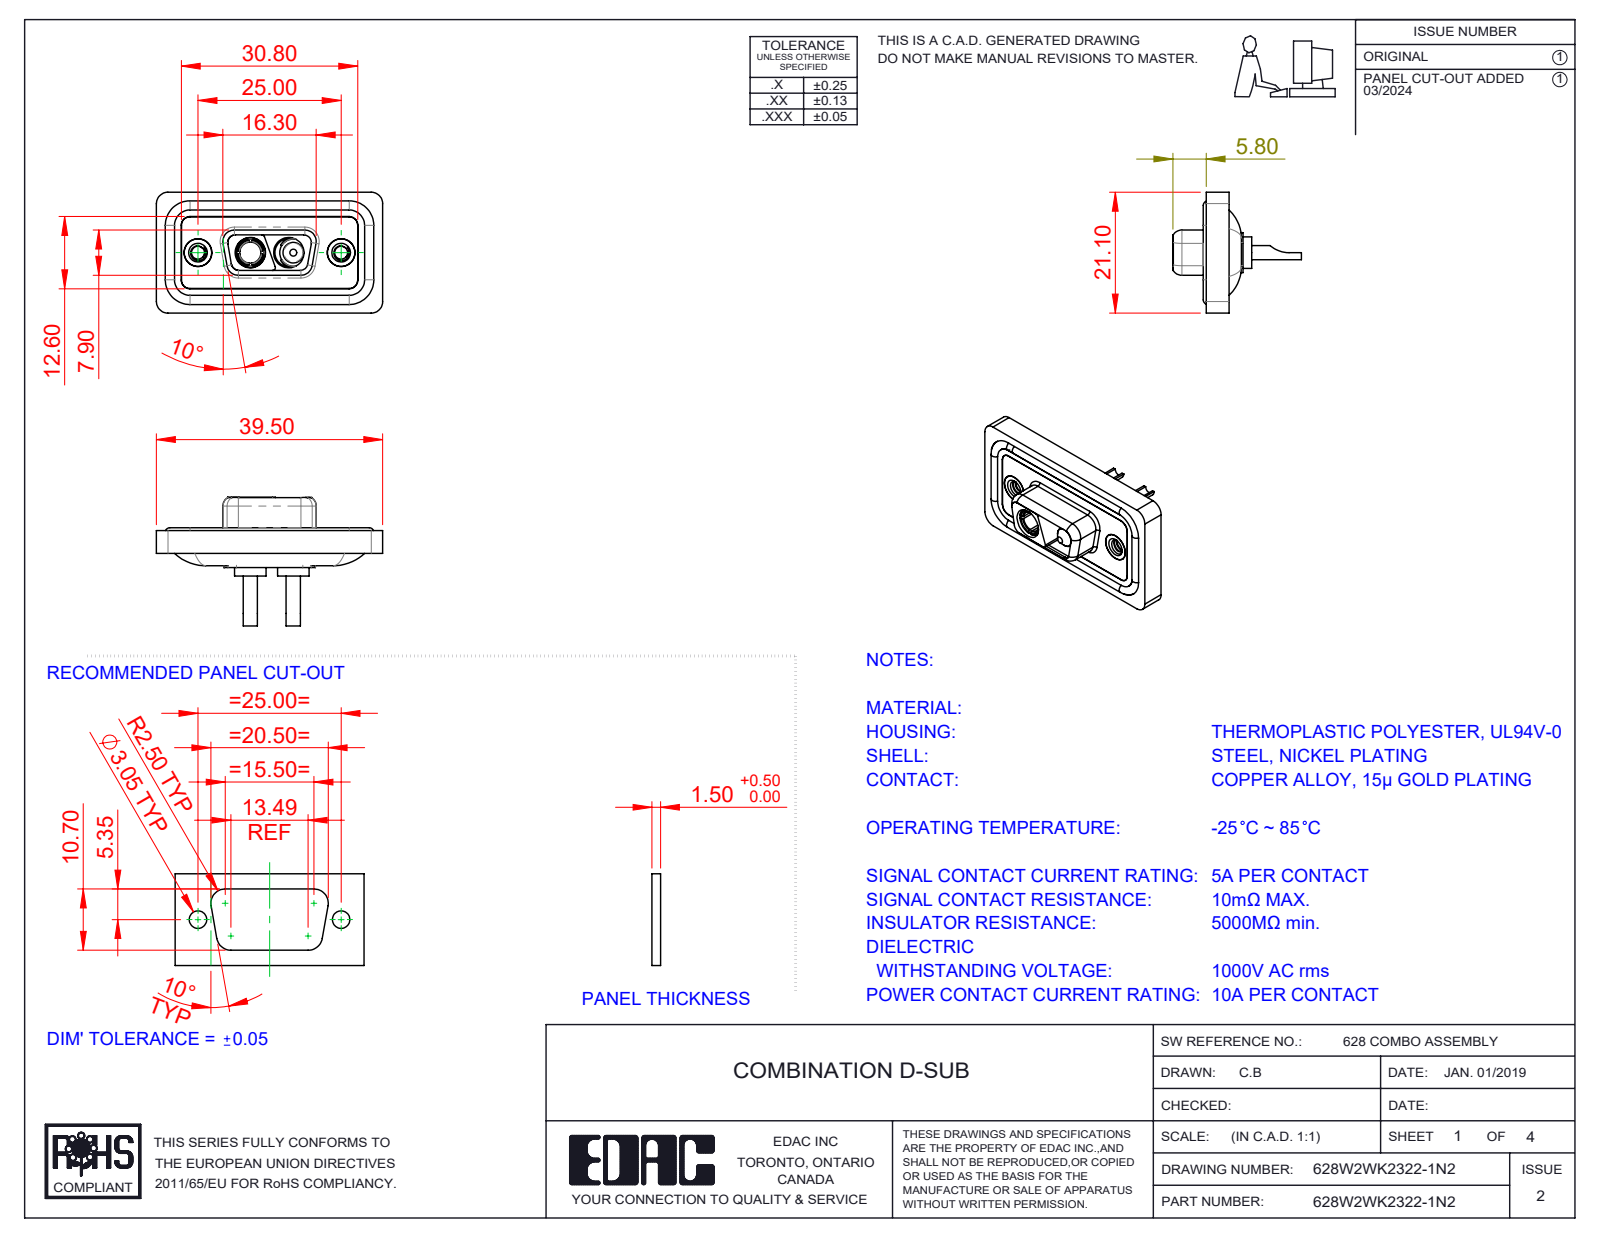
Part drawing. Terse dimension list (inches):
name: Power Socket_10A SC; 628Combo Shell Rear_09 Contacts; 628Combo Threaded Rivet_2; 628Combo Housing_2WK2 (+4 more)
written by: SolidWorks 2023 (CONFIG_CONTROL_DESIGN)
unit: in
bodies: 11 solids, 510 faces (148 planar, 237 cylindrical, 125 other)
size: 1.555 × 0.884 × 0.831
volume: 0.281 in³; area: 11.53 in²
holes: 4× ⌀0.191, 2× ⌀0.067, 2× ⌀0.089, 2× ⌀0.157, 2× ⌀0.159, 2× ⌀0.197, 2× ⌀0.209, 1× ⌀0.146
bosses: 4× ⌀0.063, 2× ⌀0.217, 2× ⌀0.205, 2× ⌀0.195, 2× ⌀0.189, 2× ⌀0.187, 2× ⌀0.148, 2× ⌀0.098
rounds: 22× R0.059, 18× R0.079, 8× R0.053, 8× R0.063, 6× R0.02, 4× R0.01, 4× R0.024, 4× R0.026
face distances: 0.016, 0.043, 0.114, 0.063, 0.02, 0.071, 0.222, 0.059, 0.211, 0.122
hole spacings: 0.36, 0.624, 0.265, 0.984
